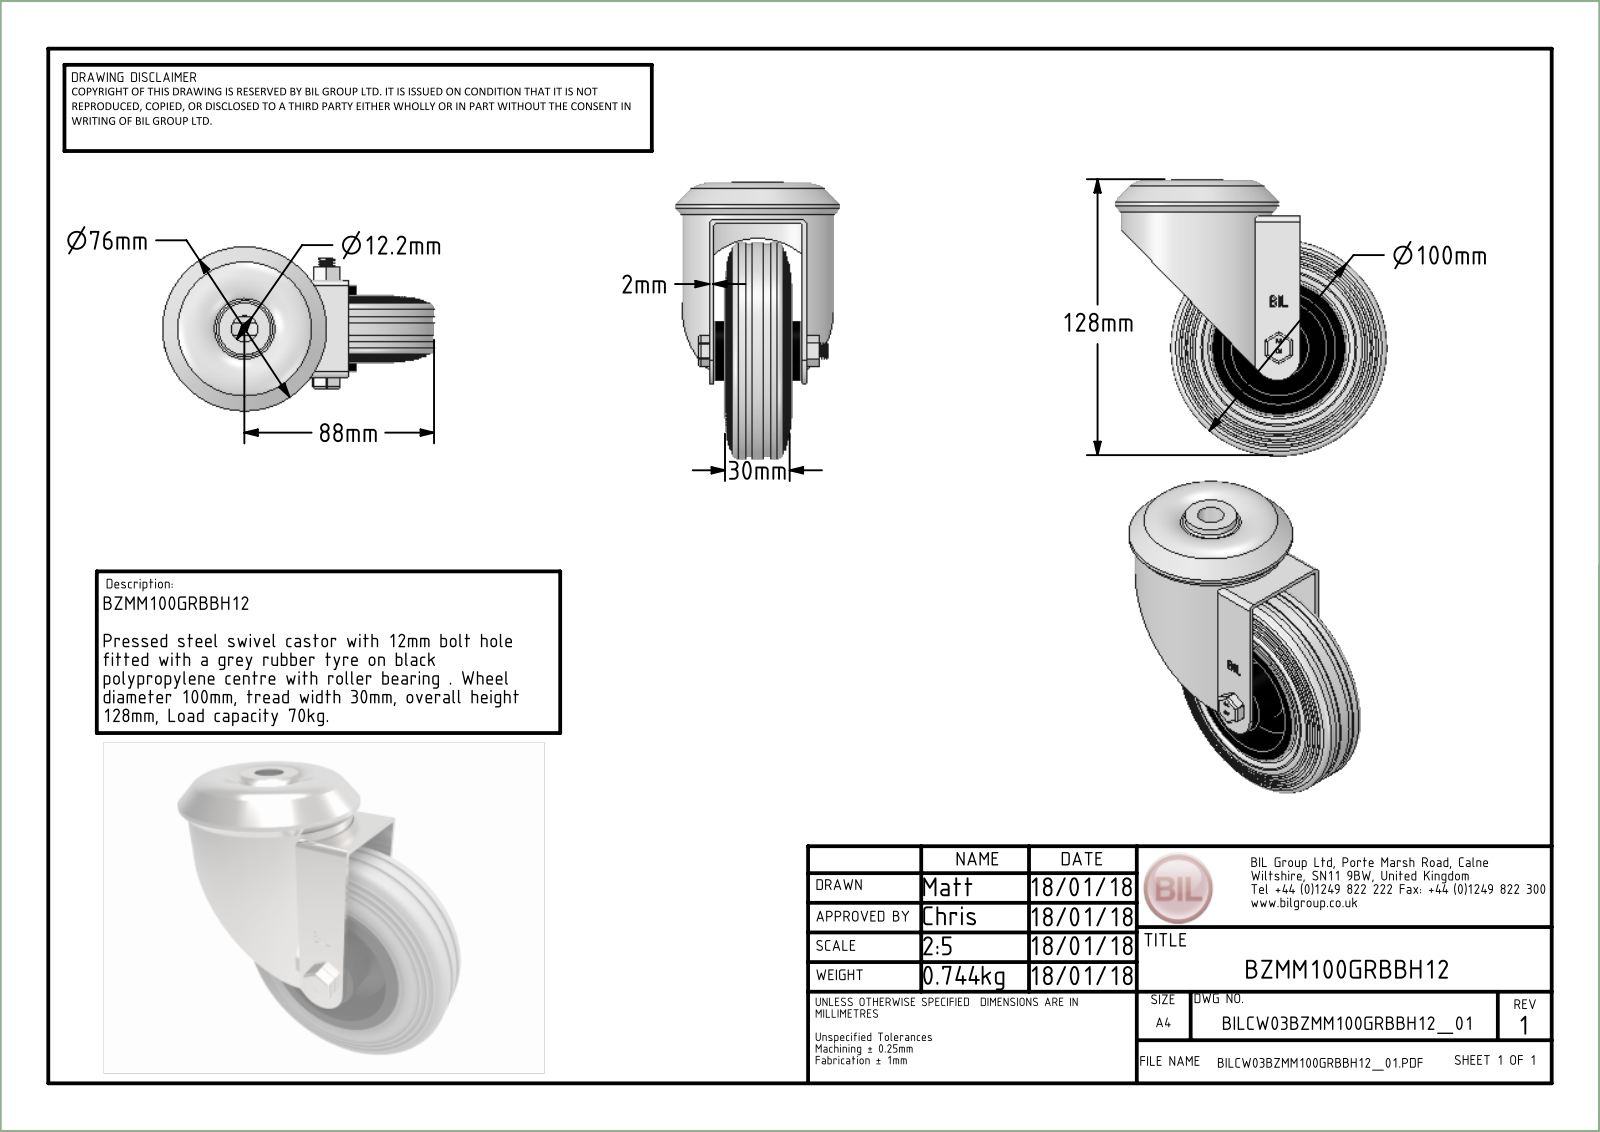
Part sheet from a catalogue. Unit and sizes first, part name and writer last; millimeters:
Units: millimetres
Overall size (bounding box): 128 × 126 × 76
Round holes (diameter × count): ⌀0.66 ×2, ⌀8 ×1, ⌀8.2 ×1, ⌀8.4 ×1, ⌀8.6 ×1, ⌀12 ×1, ⌀12.2 ×1, ⌀13 ×1, ⌀22 ×1, ⌀25 ×1, ⌀50.79 ×1, ⌀65 ×1
Round bosses / shafts (diameter × count): ⌀4.5 ×8, ⌀100 ×1, ⌀99 ×1, ⌀70 ×1, ⌀61.5 ×1, ⌀49.5 ×1, ⌀38 ×1, ⌀28 ×1
Partial cylindrical surfaces — rounded edges, fillets, slot ends (radius × count): R0.5 ×18, R0.25 ×12, R0.33 ×4, R0.64 ×4, R1.25 ×4, R0.63 ×2, R0.64 ×2, R2.5 ×2
Main face-to-face distances: 2.5, 18.75, 42.5, 3, 7.5, 16.25, 26.25, 23.75, 40, 32.63
Hole centre spacings: 3.22, 2.49
Volume: 246 373 mm³ · Surface area: 103 587 mm²
Bodies: 18 solids, 523 faces (190 planar, 161 cylindrical, 172 other)
Part name (STEP PRODUCT): BZMM100GRBBH12 v3; BZMM100ASBH12 v1; ZINC PLATED PRESSED STEEL HEAD; ZINC PLATED, PRESSED STEEL FORKS (+7 more)
STEP written by: Autodesk Translation Framework v13.20.0.188 (AUTOMOTIVE_DESIGN)
